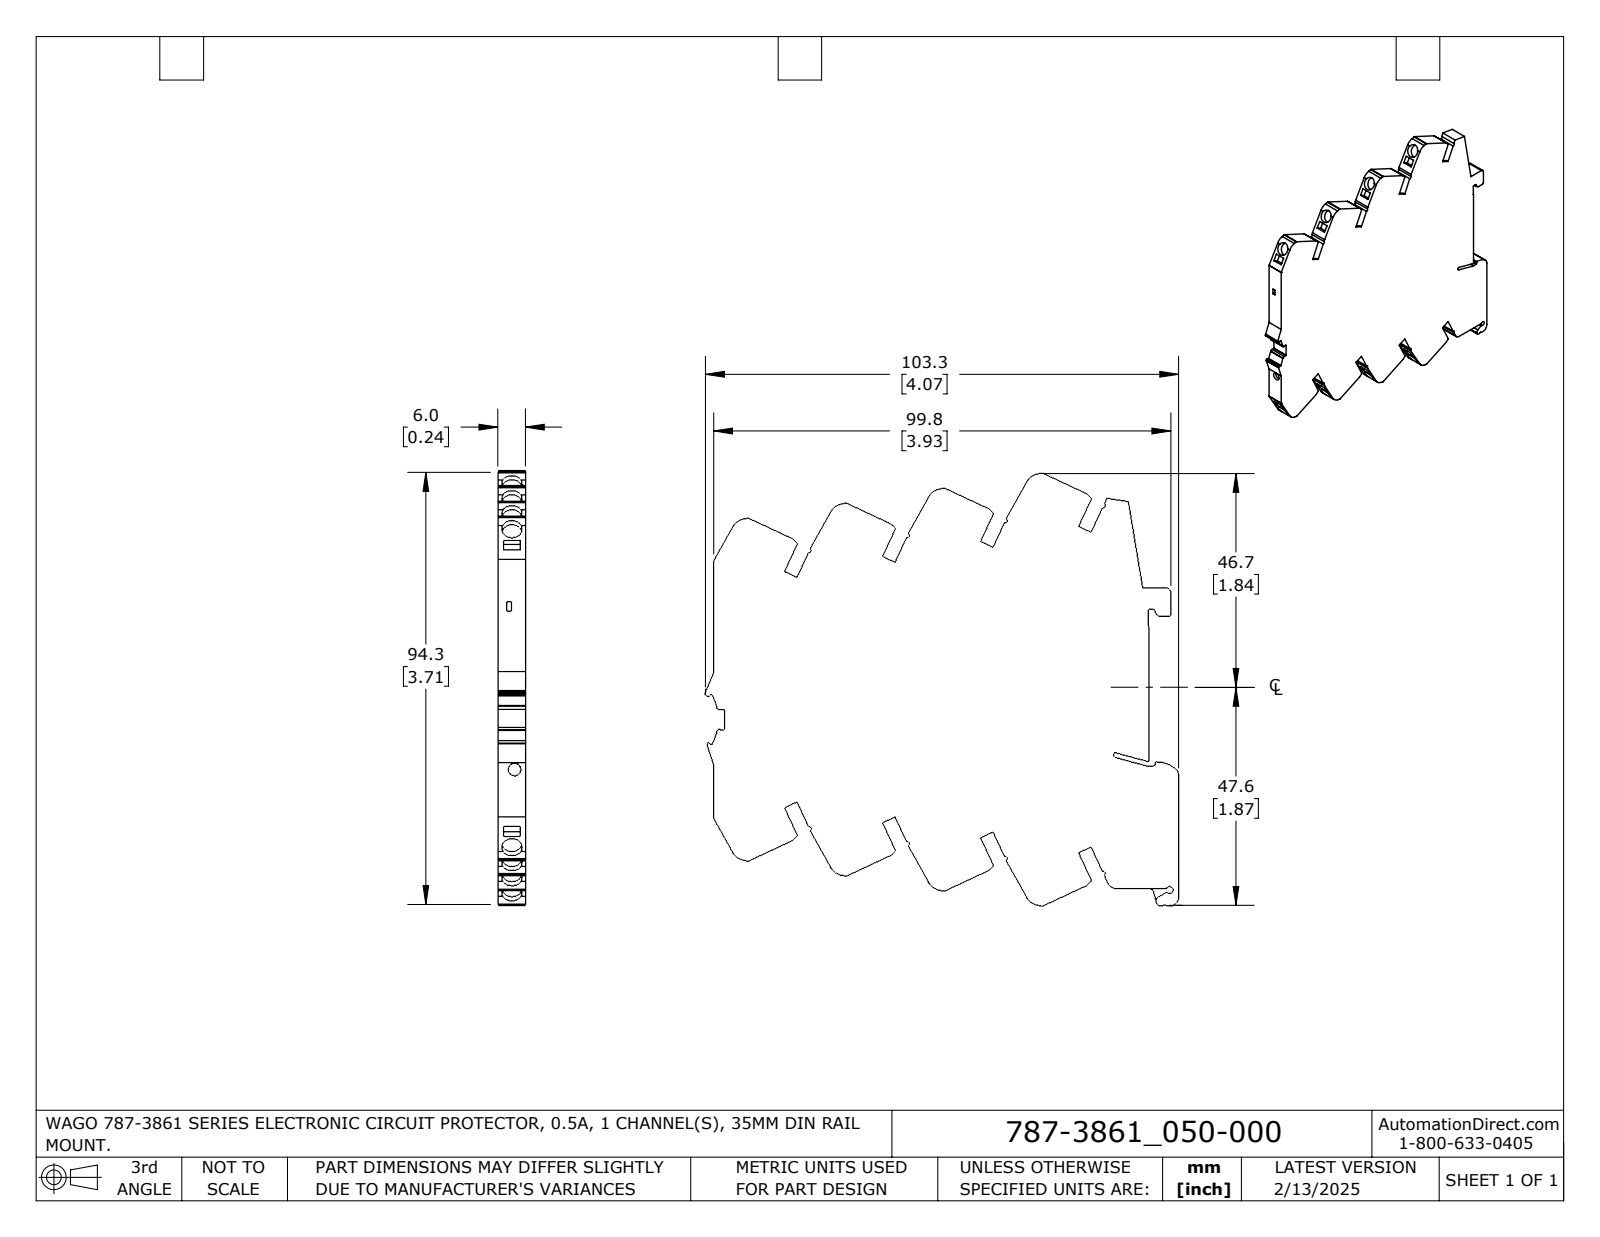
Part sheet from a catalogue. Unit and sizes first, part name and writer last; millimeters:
Units: millimetres
Overall size (bounding box): 103.3 × 94.26 × 6
Round holes (diameter × count): ⌀4.4 ×8, ⌀2.7 ×1
Partial cylindrical surfaces — rounded edges, fillets, slot ends (radius × count): R0.2 ×13, R0.5 ×12, R0.4 ×8, R3.35 ×8, R1 ×5, R0.3 ×3, R2 ×3, R0.45 ×2
Main face-to-face distances: 6, 17.99, 17.02, 12.01, 3, 35.98, 12, 24.01, 14.99, 34.04
Hole centre spacings: 13.35, 13.34, 26.7, 26.71, 40.05
Volume: 43 992 mm³ · Surface area: 18 864 mm²
Bodies: 1 solid, 262 faces (197 planar, 65 cylindrical, 0 other)
Part name (STEP PRODUCT): 787-3861_050-000_HI
STEP written by: SolidWorks 2024 (AUTOMOTIVE_DESIGN)
